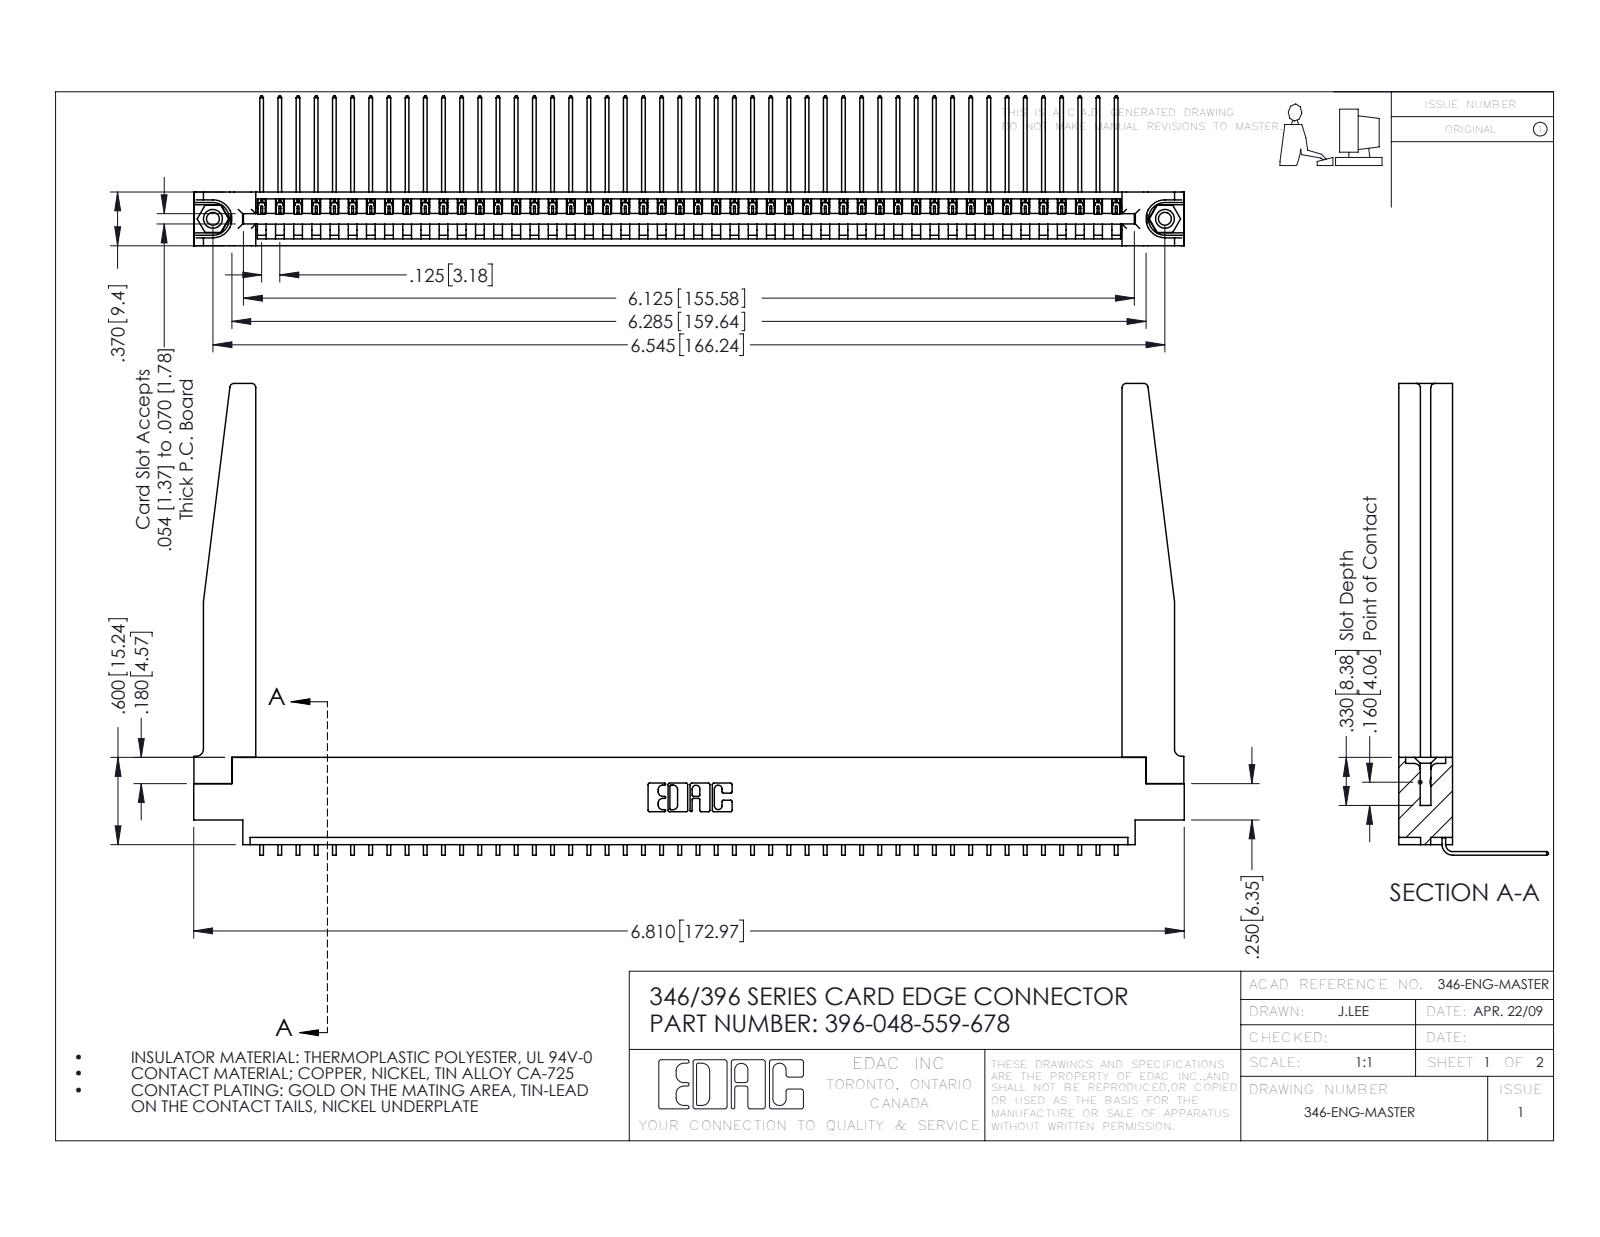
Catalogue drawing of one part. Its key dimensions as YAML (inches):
part_name: "396-048-559-678; 345-292-001_558 559 Tail - 1; 346 Part_0.170 Offset - 0.156 Dia-TH; 345-250-001_345-250-001-102 (+1 more)"
step_written_by: "SolidWorks 2016 (CONFIG_CONTROL_DESIGN)"
units: inches
bodies: {solids: 53, faces: 3240, planar: 2238, cylindrical: 950, other: 52}
overall_size: [6.81, 3.243, 1.03]
volume: 1.435
surface_area: 44.13
round_holes:
  - {diameter: 0.089, count: 2}
  - {diameter: 0.125, count: 2}
  - {diameter: 0.156, count: 2}
  - {diameter: 0.064, count: 1}
round_bosses_or_shafts:
  - {diameter: 0.155, count: 2}
partial_cylinders:
  - {radius: 0.006, count: 96}
  - {radius: 0.01, count: 22}
  - {radius: 0.03, count: 8}
  - {radius: 0.007, count: 6}
  - {radius: 0.031, count: 6}
  - {radius: 0.026, count: 3}
  - {radius: 0.05, count: 3}
  - {radius: 0.031, count: 2}
face_to_face_distances: [0.37, 0.048, 0.322, 0.072, 0.148, 0.025, 0.15, 0.25, 0.298, 0.222]
hole_center_spacings: [0.246, 6.336, 6.545]
